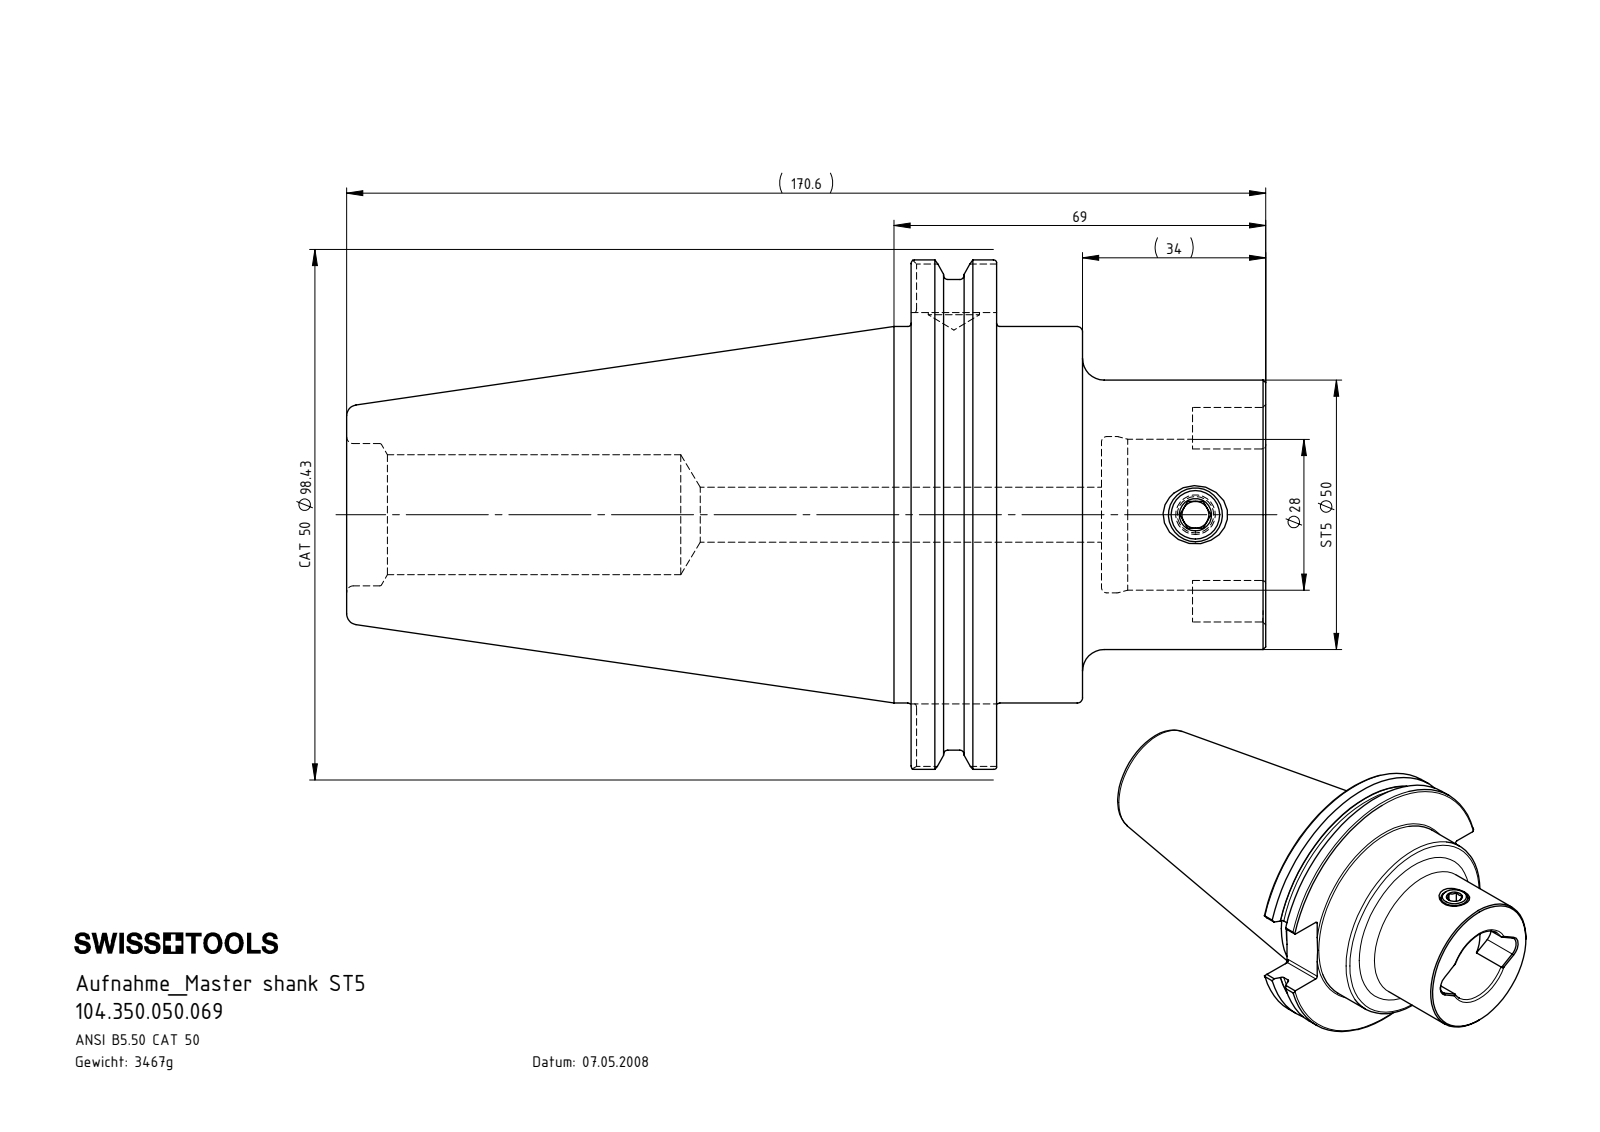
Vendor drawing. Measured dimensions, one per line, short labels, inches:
name: ST5-ER1.001.012_A; CT5-ST5.K01.069_A; CT5-ST5.K01.069
written by: SolidWorks 2015 (CONFIG_CONTROL_DESIGN)
unit: in
bodies: 2 solids, 140 faces (44 planar, 39 cylindrical, 57 other)
size: 6.717 × 3.875 × 3.721
volume: 26.95 in³; area: 84.72 in²
holes: 1× ⌀0.354, 1× ⌀0.374, 1× ⌀0.402, 1× ⌀0.876, 1× ⌀1.039, 1× ⌀1.102, 1× ⌀1.142
bosses: 1× ⌀3.875, 1× ⌀3.583, 1× ⌀2.75, 1× ⌀1.969, 1× ⌀0.394
rounds: 8× R0.031, 2× R0.165
face distances: 0.625, 2.591, 1.967, 1.253, 0.628, 1.339, 1.391, 0.766, 0.138, 1.201
